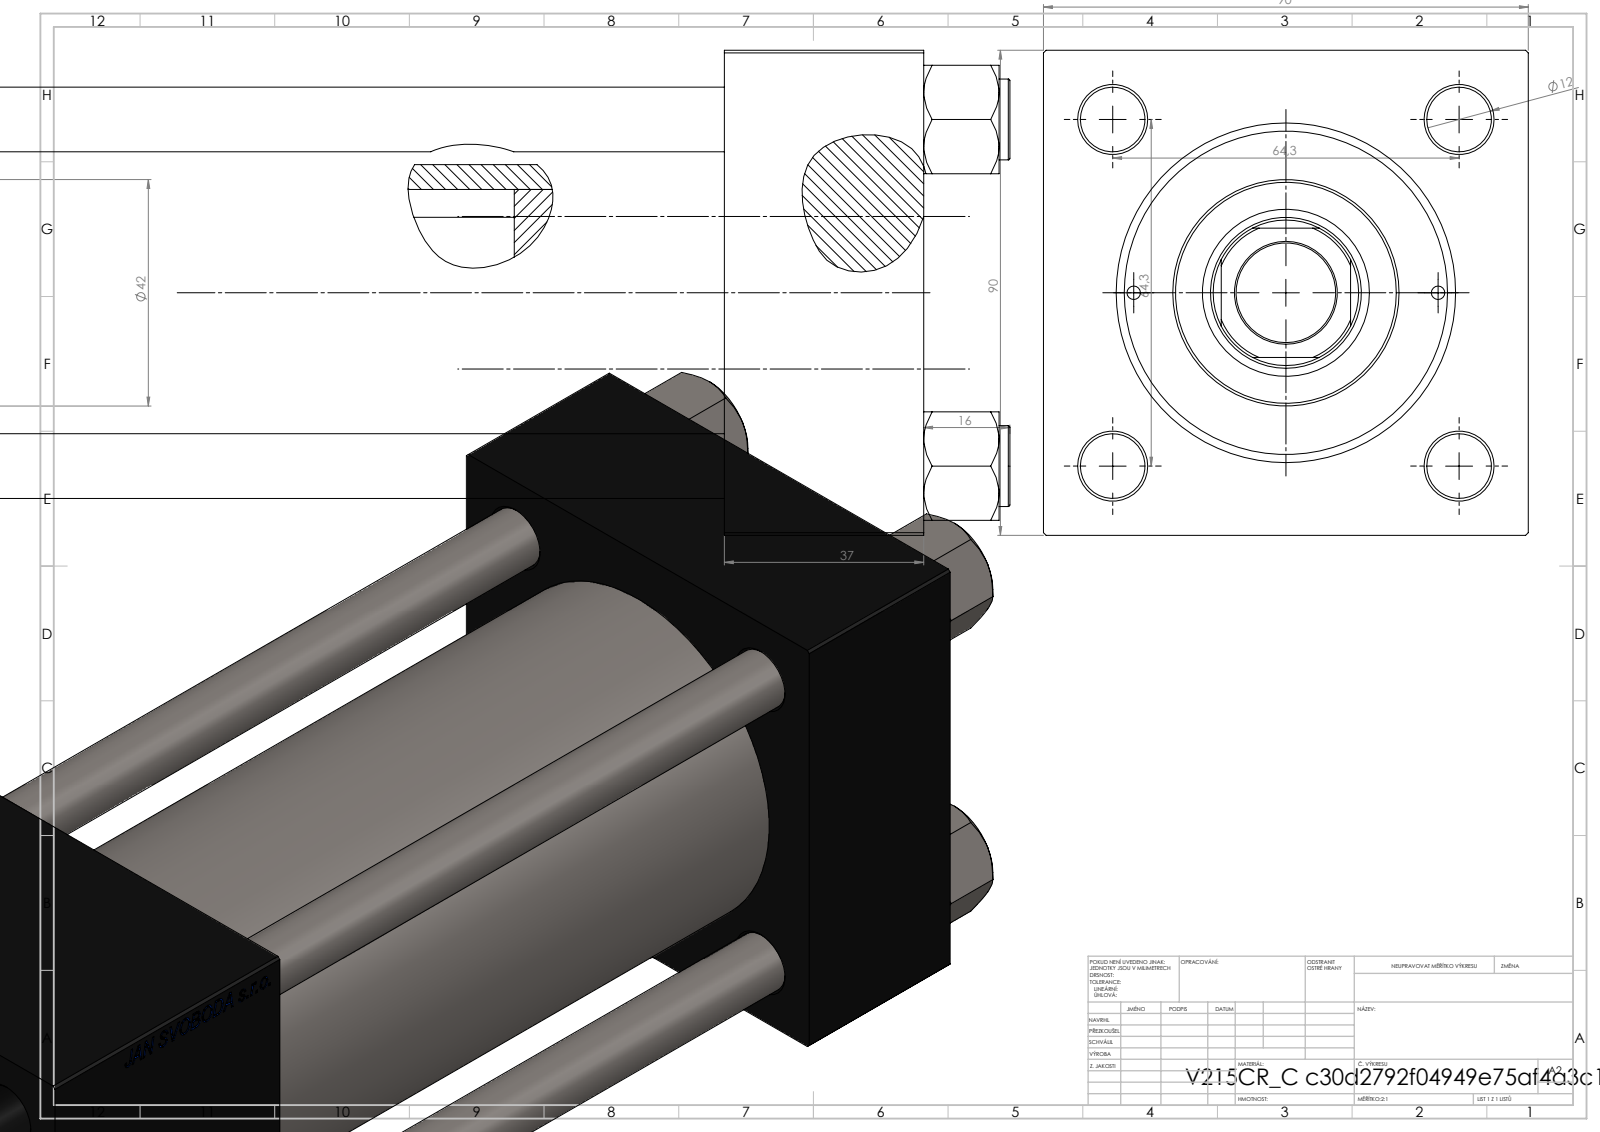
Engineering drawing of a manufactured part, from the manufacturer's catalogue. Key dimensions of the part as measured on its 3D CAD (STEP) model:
Part name (STEP PRODUCT): NUT_M5_C; V215CR_VCP_C; V215_VC_A; V215CR_C_Body (+1 more)
STEP written by: SolidWorks 2019 (CONFIG_CONTROL_DESIGN)
Units: millimetres
Bodies: 11 solids, 1154 faces (528 planar, 90 cylindrical, 536 other)
Overall size (bounding box): 283 × 90 × 90
Volume: 1 082 000 mm³ · Surface area: 231 483 mm²
Round holes (diameter × count): ⌀12 ×4, ⌀2.5 ×2, ⌀7 ×2, ⌀20.96 ×2, ⌀30 ×2, ⌀18.5 ×1, ⌀28 ×1, ⌀31 ×1, ⌀50 ×1, ⌀60 ×1, ⌀63 ×1
Round bosses / shafts (diameter × count): ⌀15 ×4, ⌀69 ×1, ⌀42 ×1
Partial cylindrical surfaces — rounded edges, fillets, slot ends (radius × count): R13.5 ×1
Main face-to-face distances: 90, 37, 235, 198, 176, 139, 59, 206.3, 169.3, 30.3
Hole centre spacings: 32.39, 45.47, 64.3, 68.42, 28.25, 90.93, 56.5, 177.5
